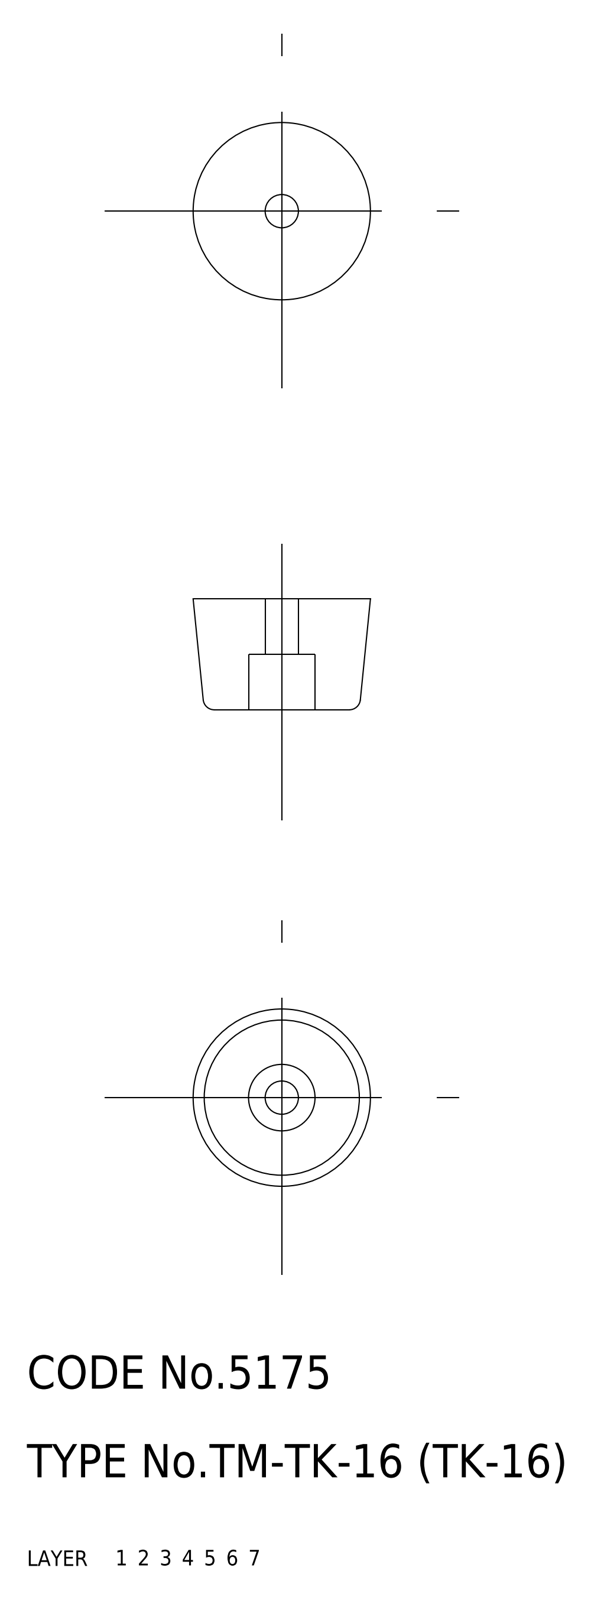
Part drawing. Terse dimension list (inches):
name: washer; rubber foot; TK_16_9222_36
written by: CADfix (AUTOMOTIVE_DESIGN)
unit: in
bodies: 2 solids, 20 faces (0 planar, 0 cylindrical, 20 other)
size: 0.63 × 0.63 × 0.394
volume: 0.097 in³; area: 1.7 in²
